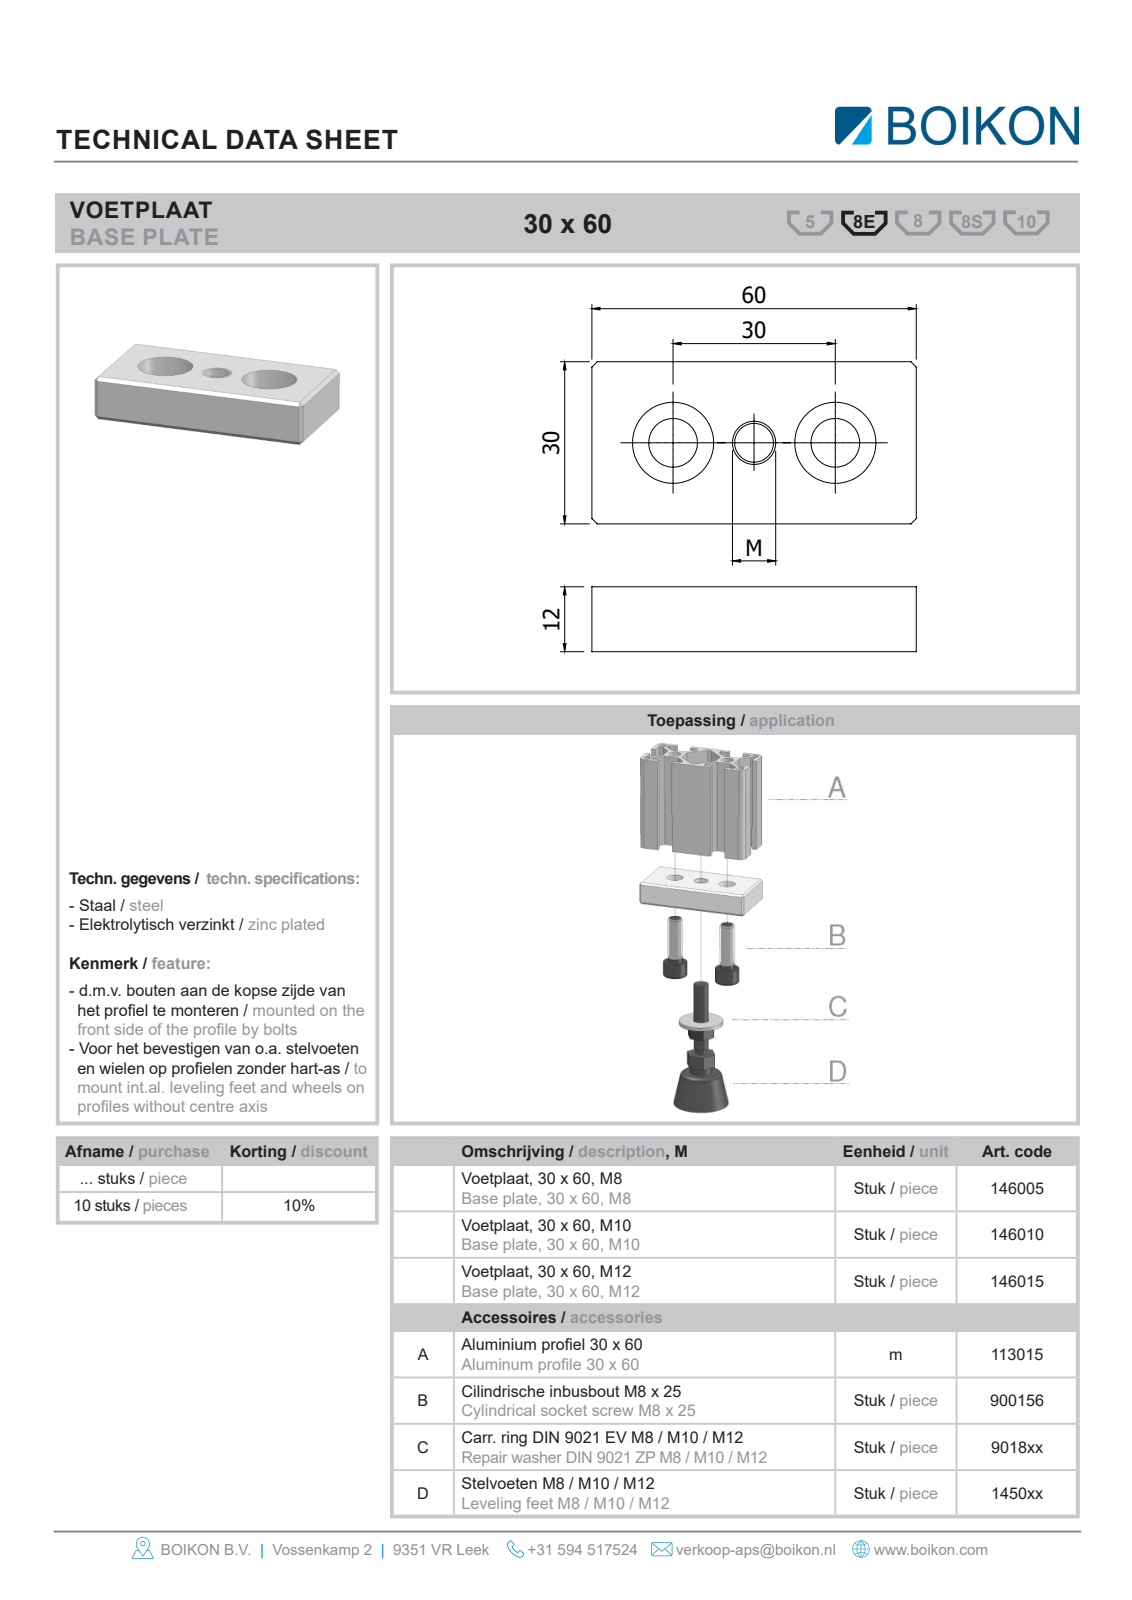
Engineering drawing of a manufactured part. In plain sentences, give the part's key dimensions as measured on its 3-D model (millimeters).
The part is named "Root; 146005Voetplaat 30x60 M8BOIKON0; 900156Cil. inbusbout DIN 912 EV M8 x 25BOIKON0". Its 3-D file was written by "HiCAD 2013 1802.4 Build 509 (AUTOMOTIVE_DESIGN)". It is 3 solids with 55 faces: 38 planar, 11 cylindrical and 6 other. Overall it measures 60 by 34 by 30 millimeters. Its volume is 21 012 cubic millimeters and its surface area 9 074 square millimeters. Round holes: 2 of diameter 9, 2 of diameter 15, 1 of diameter 8. Round bosses or shafts: 2 of diameter 13, 2 of diameter 8, 2 of diameter 6.47. The main face-to-face distances are 12, 30, 9, 3, 60, 11, 8, 1, 6, 22. The hole center spacings are 15, 30.
